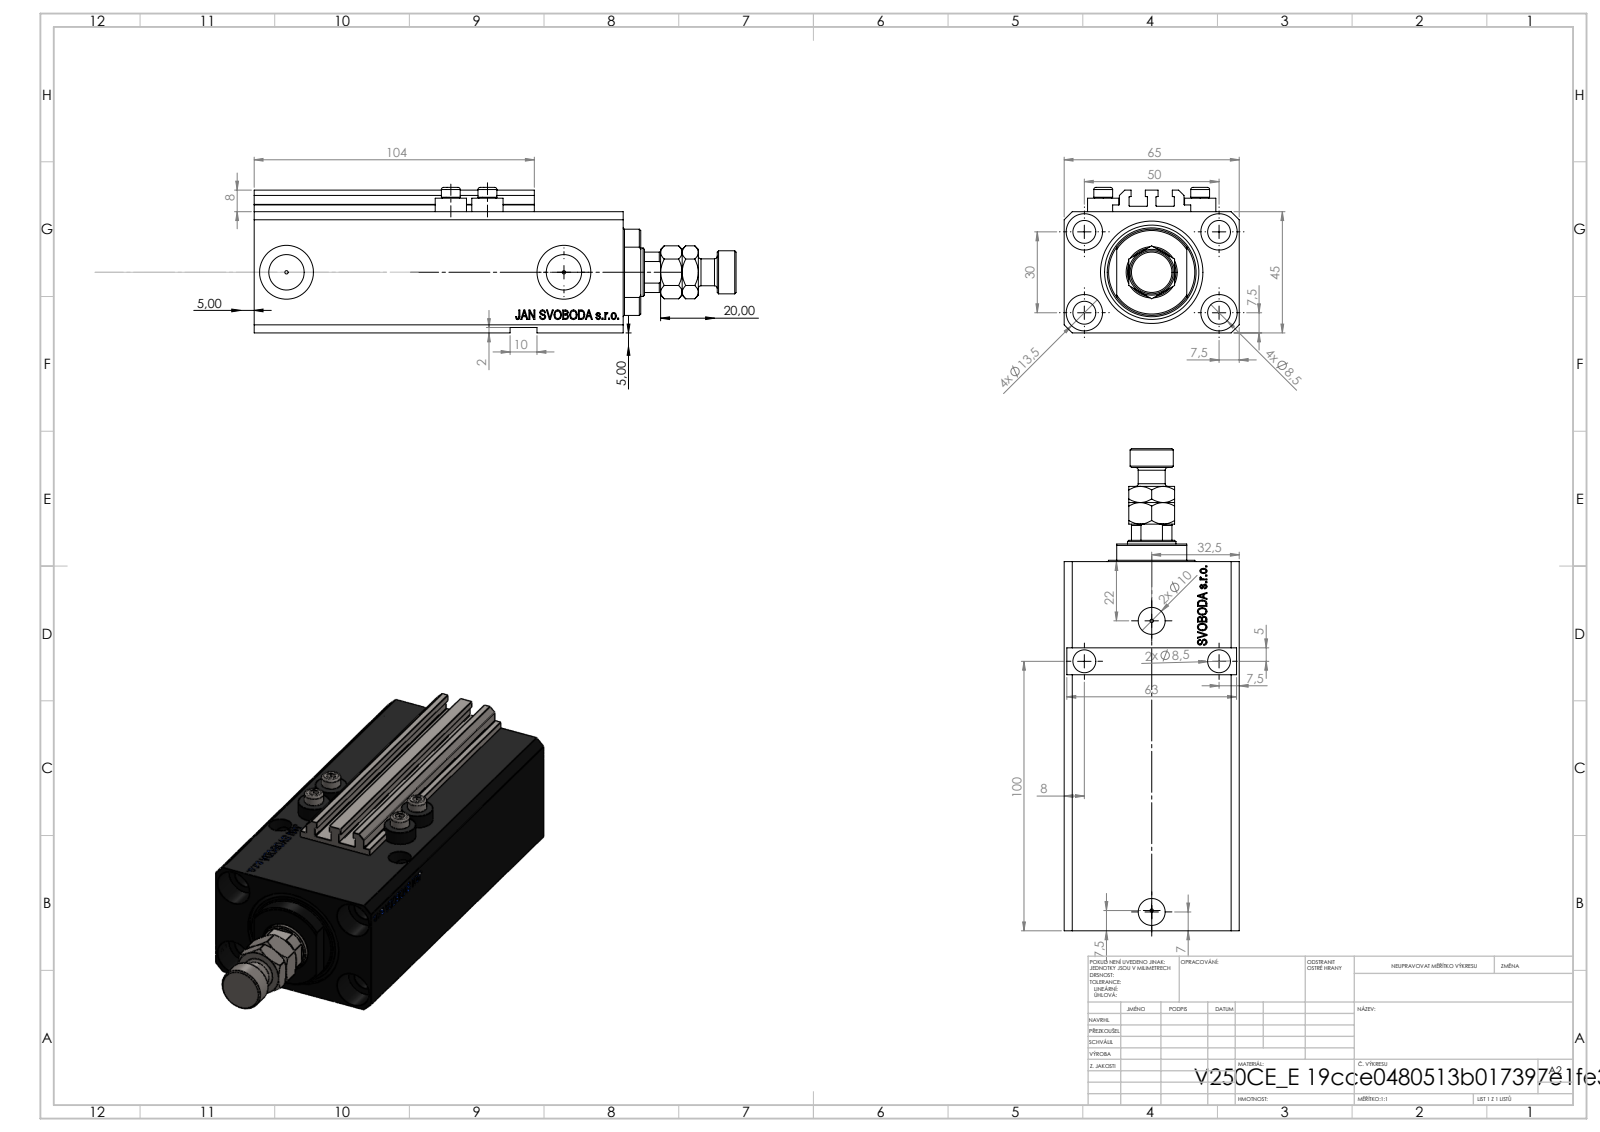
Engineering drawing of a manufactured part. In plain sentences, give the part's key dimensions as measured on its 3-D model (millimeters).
The part is named "ALLEN BOLT V250CE; MFA; V250CE_E_Body; V250CE_C_VCP (+1 more)". Its 3-D file was written by "SolidWorks 2019 (CONFIG_CONTROL_DESIGN)". It is 9 solids with 1139 faces: 527 planar, 150 cylindrical and 462 other. Overall it measures 179 by 65 by 54 millimeters. Its volume is 355 919 cubic millimeters and its surface area 95 611 square millimeters. Round holes: 9 of diameter 8.5, 4 of diameter 1.25, 4 of diameter 4, 4 of diameter 13.5, 2 of diameter 10, 2 of diameter 13.16, 2 of diameter 20, 1 of diameter 18, 1 of diameter 25, 1 of diameter 38. Round bosses or shafts: 4 of diameter 11.6, 4 of diameter 7, 1 of diameter 16, 1 of diameter 10. Partial cylindrical surfaces (rounded edges, fillets, slot ends): 10 of radius 0.2, 1 of radius 8.5, 1 of radius 16. The main face-to-face distances are 45, 65, 47, 14, 2, 123, 2.5, 10, 20.5, 6. The hole center spacings are 29.15, 50, 13.6, 15.12, 27.89, 30, 33.61, 33.62.
